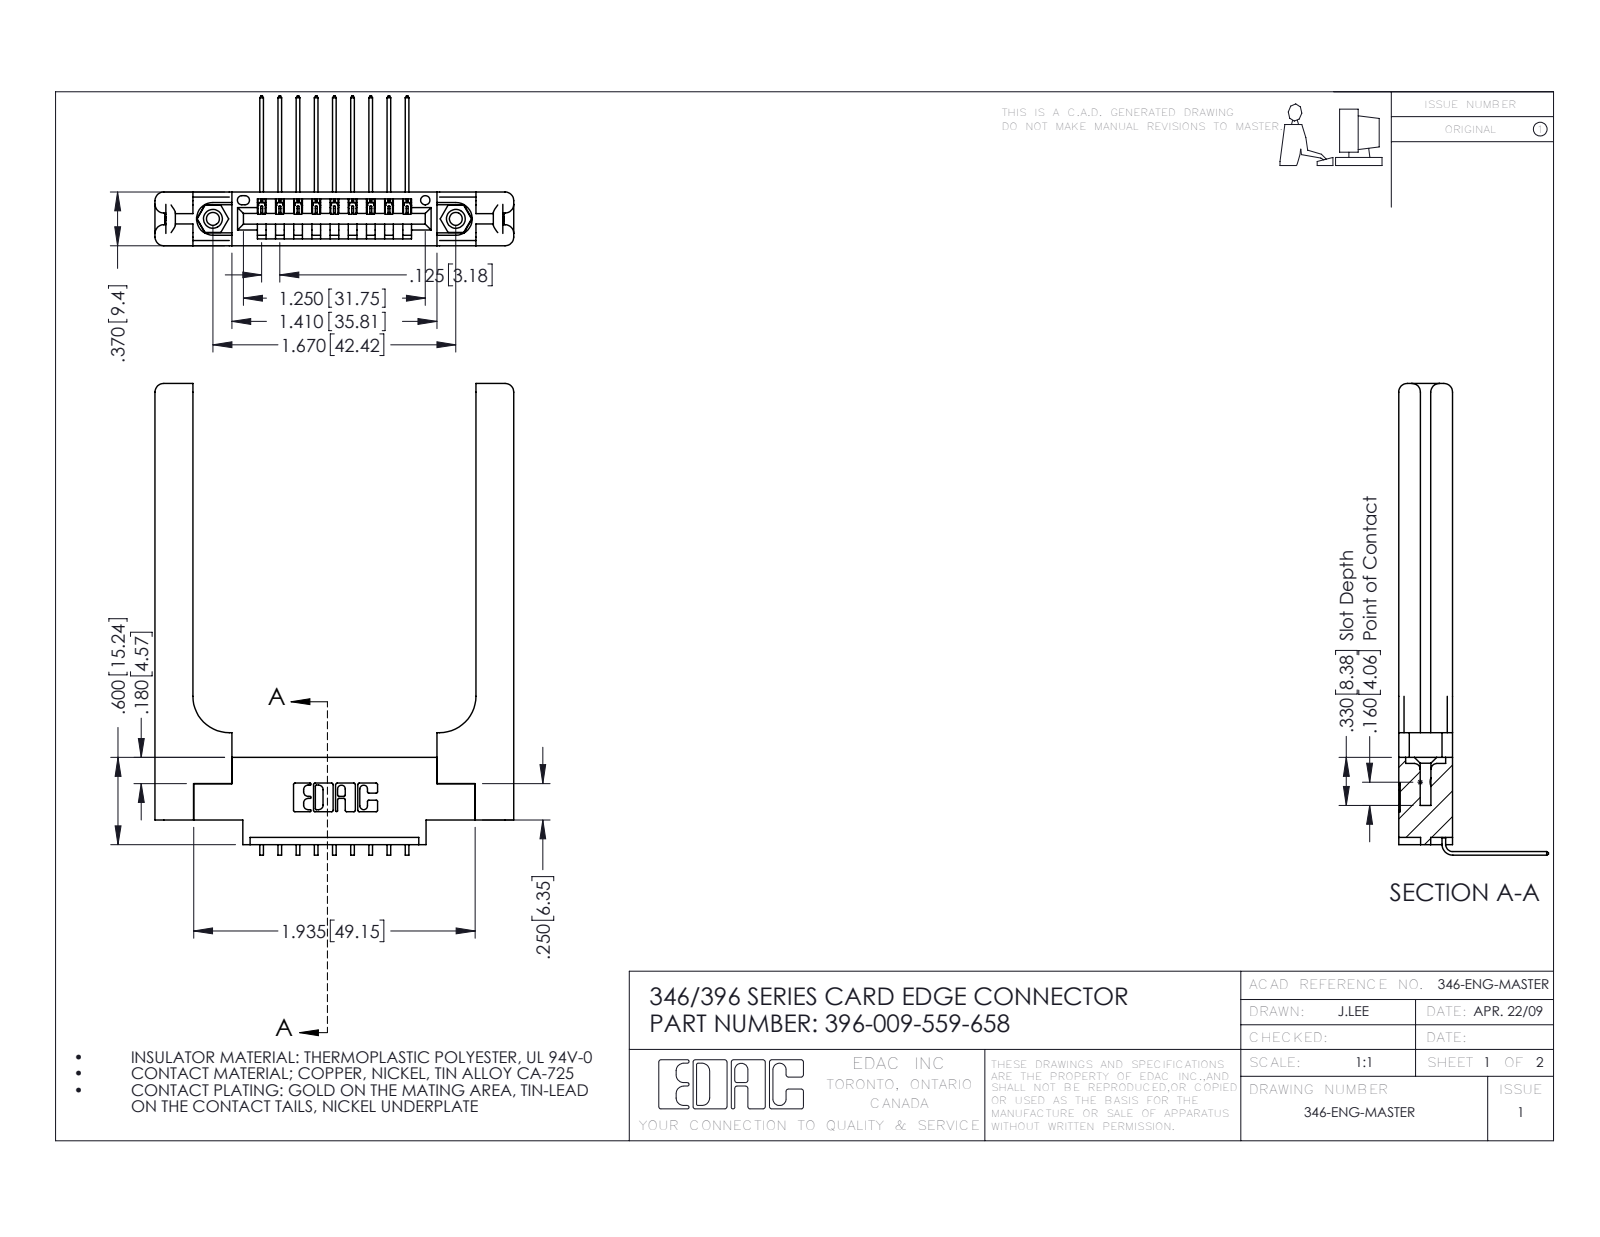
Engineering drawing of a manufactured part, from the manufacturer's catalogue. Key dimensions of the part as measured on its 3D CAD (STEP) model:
Part name (STEP PRODUCT): 345-250-001_345-250-001-102; 396-009-559-658; 346 Part_0.170 Offset - 0.156 Dia-TH; 346-220-058_345-220-058 (+1 more)
STEP written by: SolidWorks 2016 (CONFIG_CONTROL_DESIGN)
Units: inches
Bodies: 14 solids, 922 faces (606 planar, 256 cylindrical, 60 other)
Overall size (bounding box): 3.243 × 2.466 × 1.03
Volume: 0.803 in³ · Surface area: 18.92 in²
Round holes (diameter × count): ⌀0.089 ×2, ⌀0.125 ×2, ⌀0.156 ×2, ⌀0.064 ×1
Round bosses / shafts (diameter × count): ⌀0.155 ×2
Partial cylindrical surfaces — rounded edges, fillets, slot ends (radius × count): R0.01 ×22, R0.006 ×18, R0.06 ×16, R0.007 ×6, R0.031 ×6, R0.026 ×3, R0.03 ×2, R0.031 ×2
Main face-to-face distances: 0.37, 0.15, 0.072, 0.22, 0.148, 0.048, 0.25, 0.102, 0.322, 0.173
Hole centre spacings: 0.246, 1.465, 1.67
